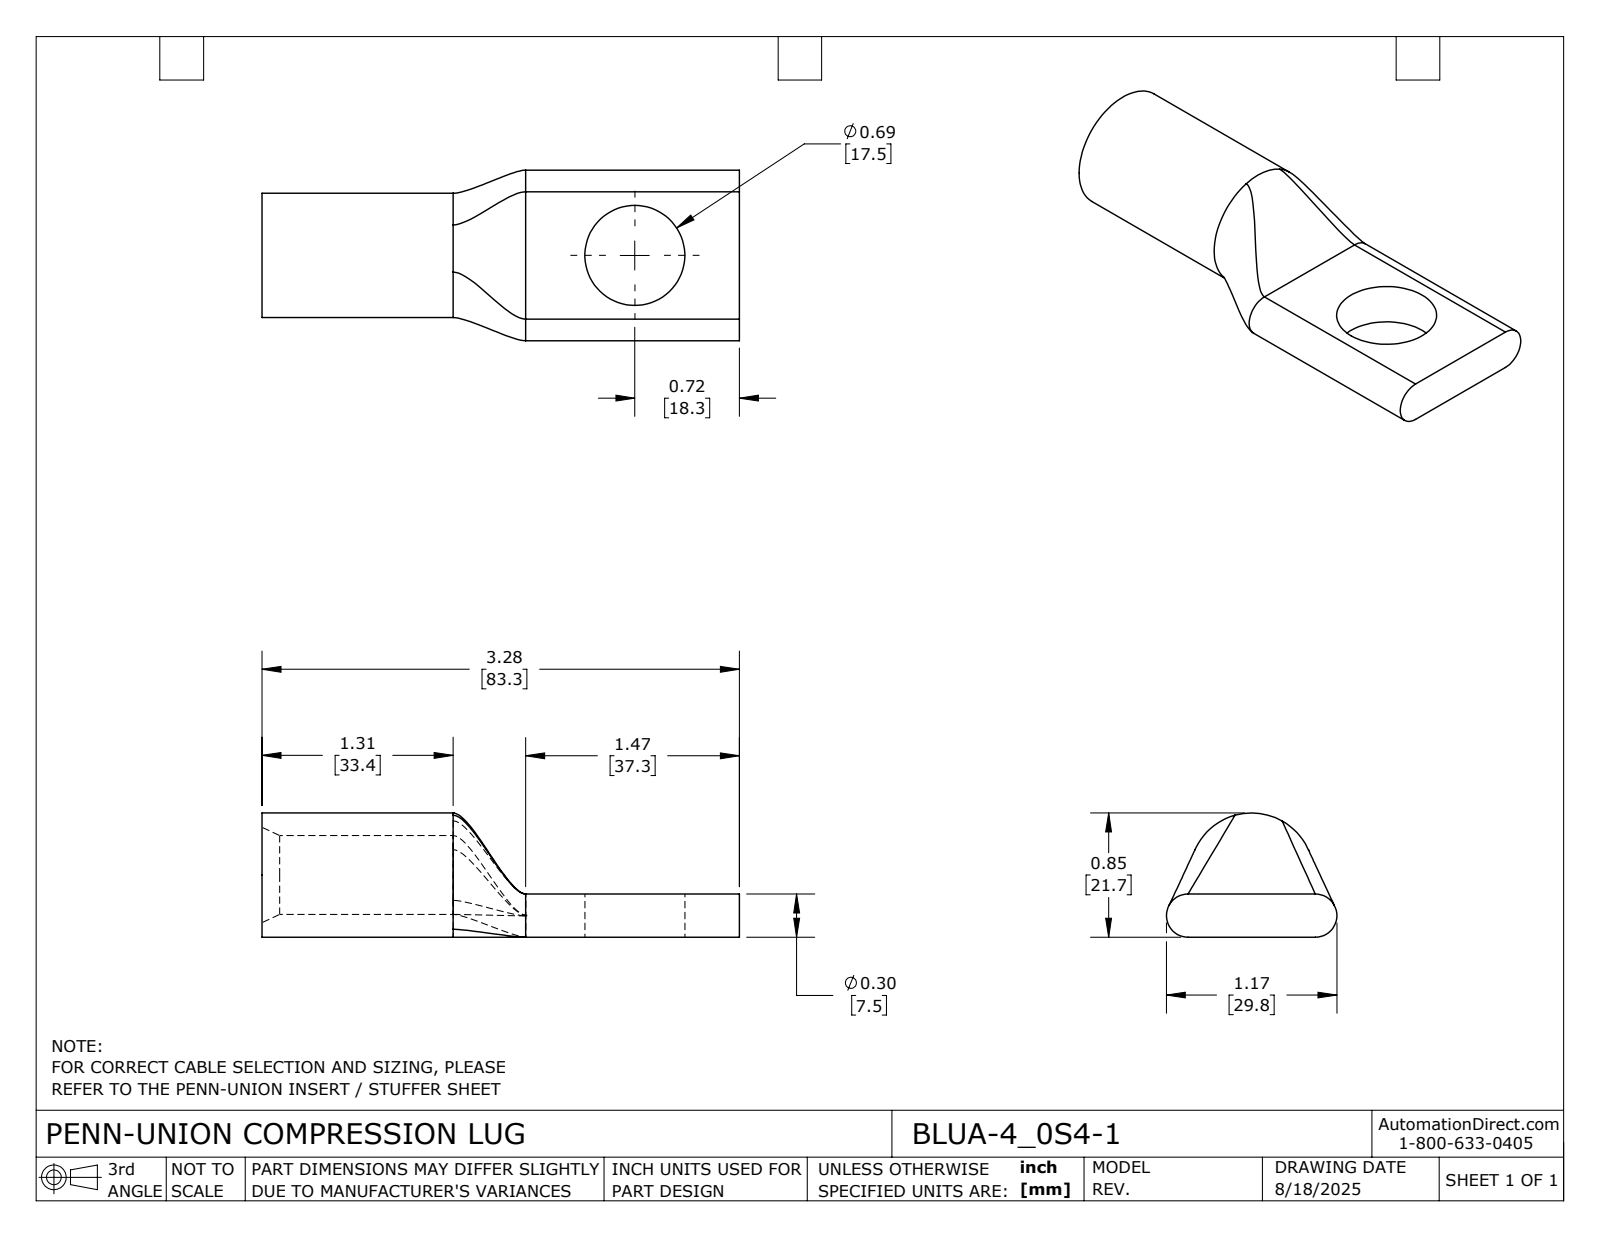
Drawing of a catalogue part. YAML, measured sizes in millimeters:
part_name: "BLUA-4_0S4-1"
step_written_by: "SolidWorks 2024 (CONFIG_CONTROL_DESIGN)"
units: millimeters
bodies: {solids: 1, faces: 24, planar: 5, cylindrical: 9, other: 10}
overall_size: [83.3, 29.8, 21.7]
volume: 16100
surface_area: 8232
round_holes:
  - {diameter: 13.8, count: 1}
  - {diameter: 17.4, count: 1}
round_bosses_or_shafts:
  - {diameter: 21.7, count: 1}
partial_cylinders:
  - {radius: 3.8, count: 2}
face_to_face_distances: [7.5, 83.3, 46.1, 37.3]
